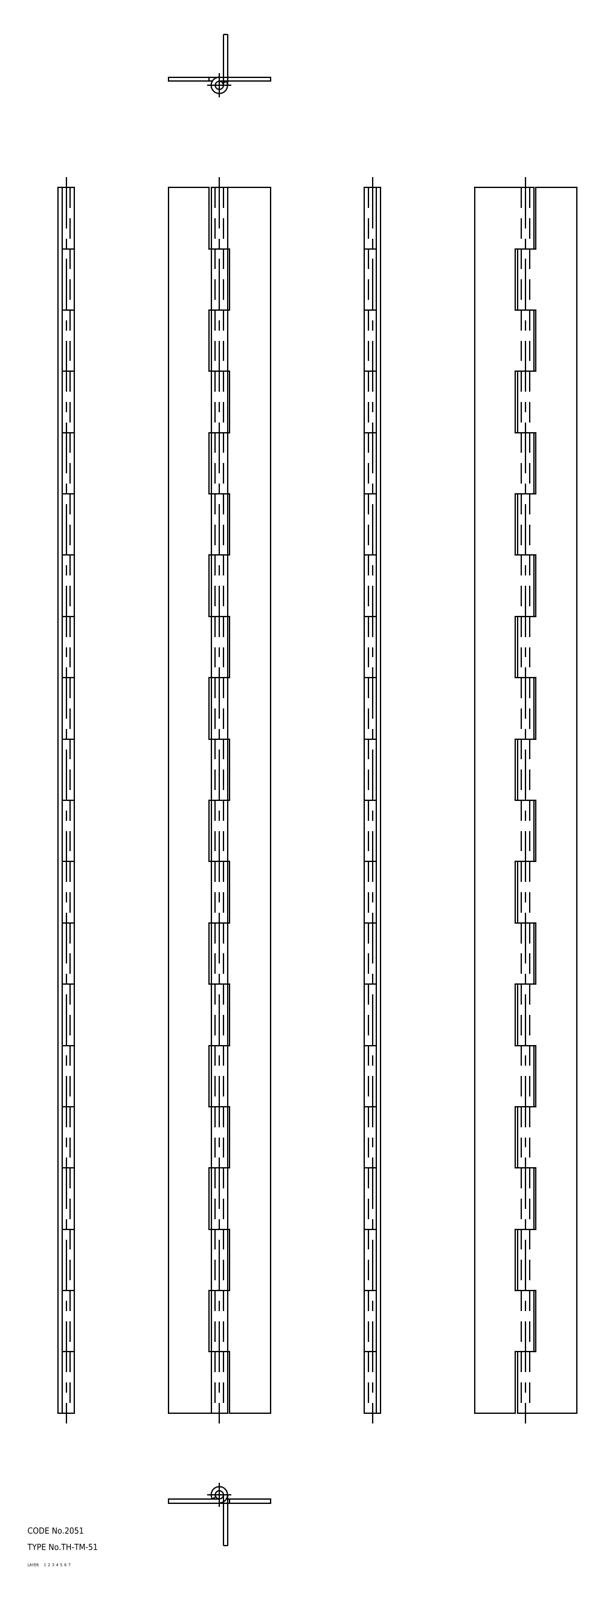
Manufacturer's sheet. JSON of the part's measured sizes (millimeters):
{"part_name": "hinge piece_B; hinge piece_A; shaft; TH_TM_51_23943_36", "step_written_by": "CADfix (AUTOMOTIVE_DESIGN)", "units": "millimeters", "bodies": {"solids": 3, "faces": 132, "planar": 0, "cylindrical": 0, "other": 132}, "overall_size": [600, 50, 8], "volume_mm3": 80353, "surface_area_mm2": 86984}
